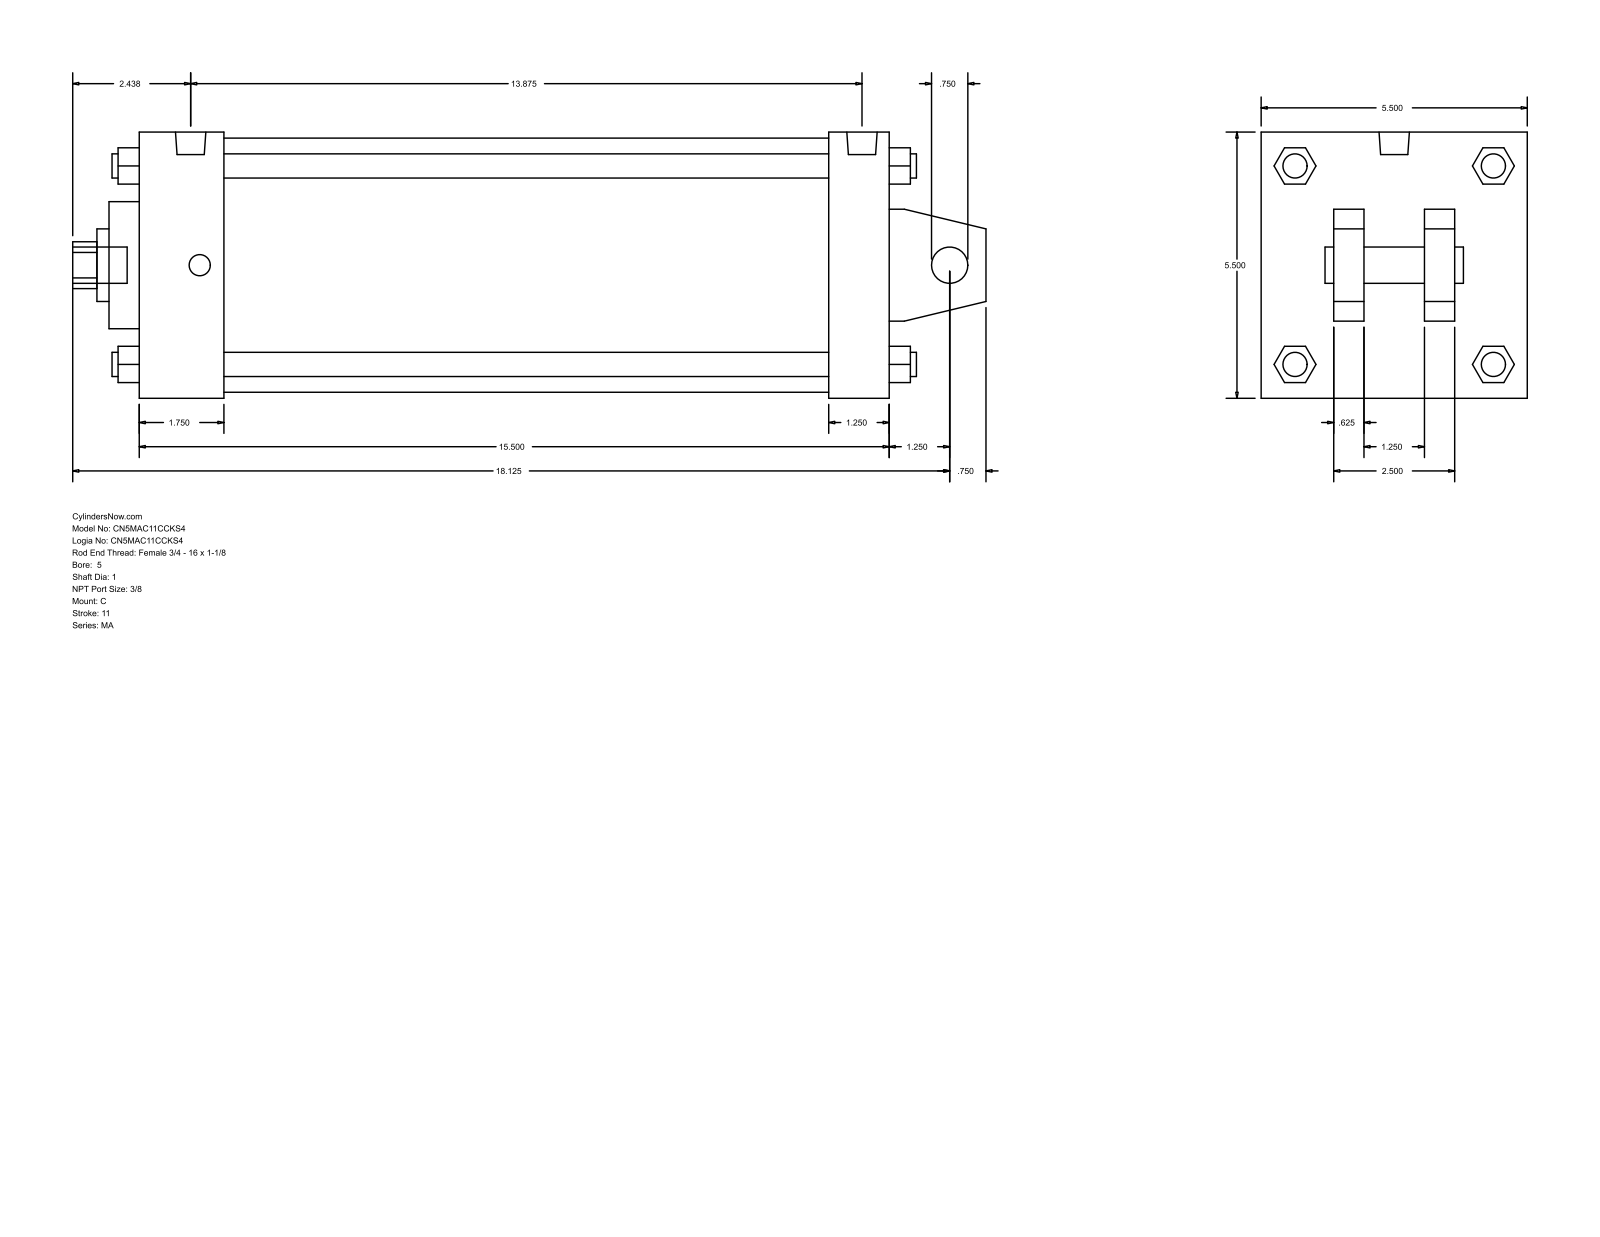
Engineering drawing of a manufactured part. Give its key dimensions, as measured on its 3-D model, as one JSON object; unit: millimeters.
{"part_name": "MA_C__0500_1", "step_written_by": "GSSL Pune (CONFIG_CONTROL_DESIGN)", "units": "millimeters", "bodies": {"solids": 0, "faces": 141, "planar": 109, "cylindrical": 32, "other": 0}, "overall_size": [479.43, 139.7, 139.7], "round_holes": [[19.05, 1], [25.4, 1], [38.1, 1], [66.67, 1], [133.35, 1]], "round_bosses_or_shafts": [[12.7, 4], [11.11, 4], [15.93, 2], [19.05, 1]], "partial_cylinders_radius": [[12.29, 1]], "face_to_face_distances": [139.7, 393.7, 15.87, 361.96, 31.74, 44.46, 317.5, 349.24, 38.1, 101.6]}
